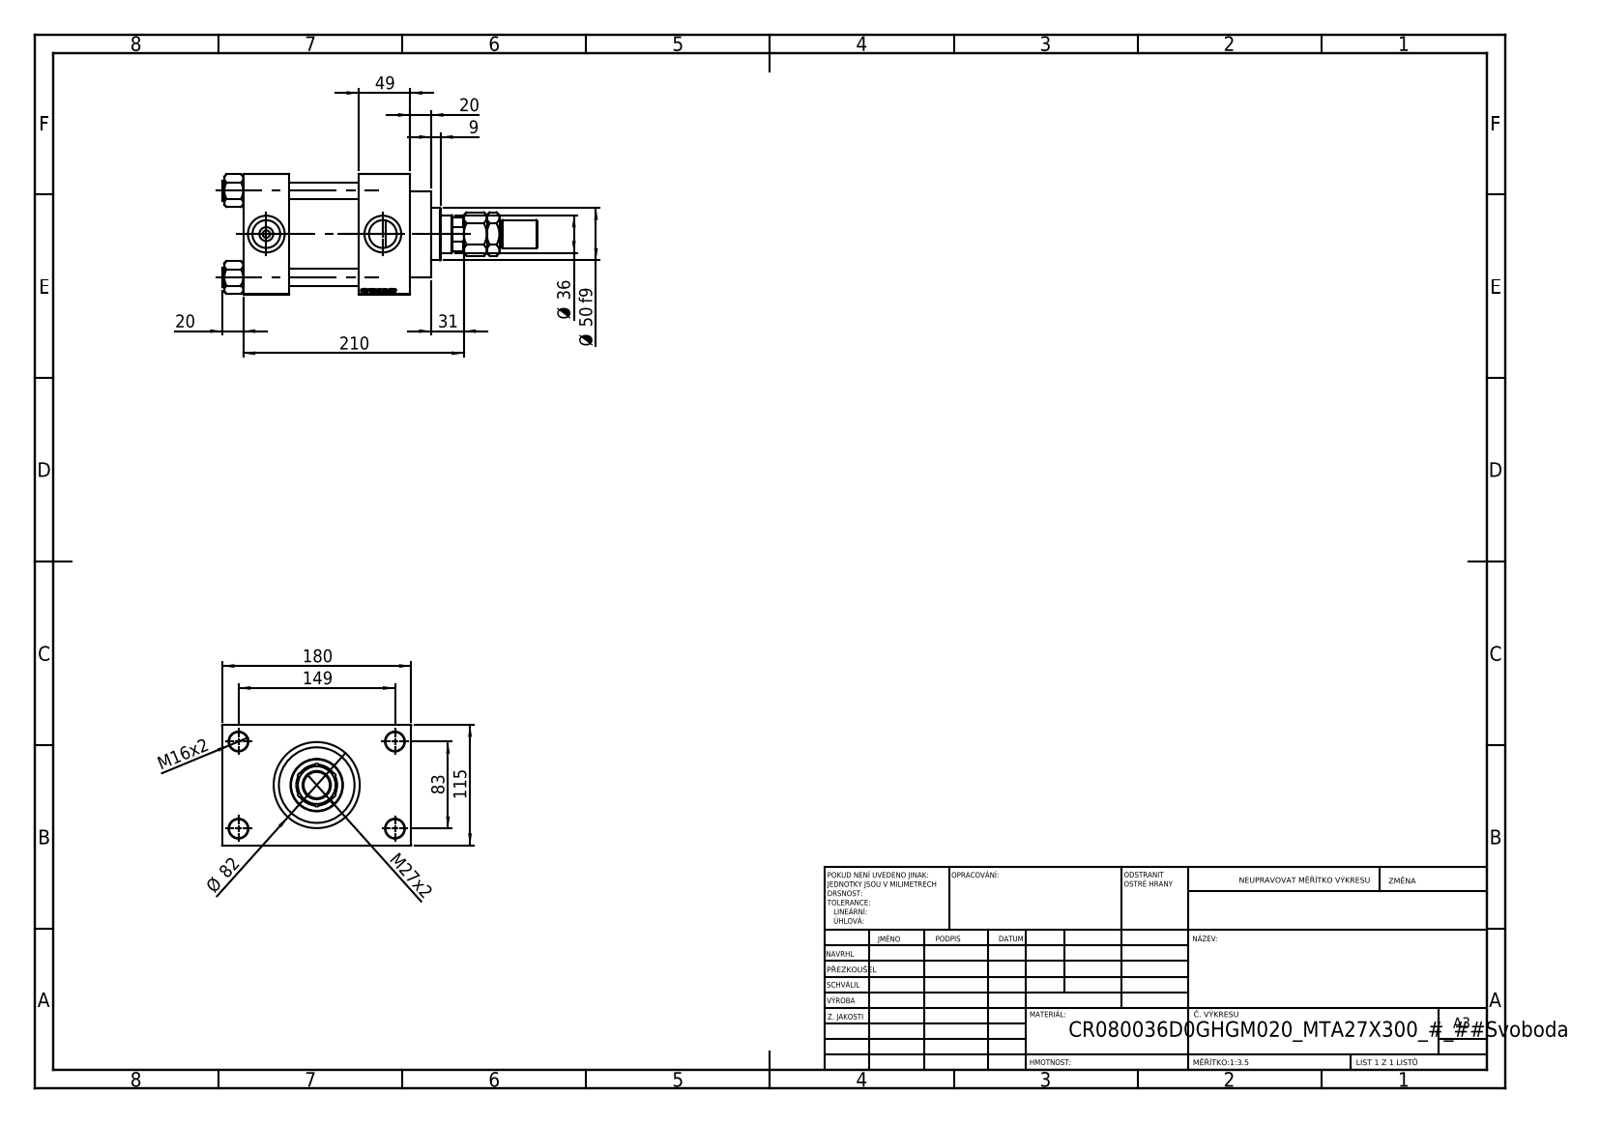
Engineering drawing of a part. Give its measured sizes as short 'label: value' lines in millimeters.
name: MTA; NUT_M5_D; V215_VC_A; V215CR_VCP_D (+2 more)
written by: SolidWorks 2019 (CONFIG_CONTROL_DESIGN)
unit: mm
bodies: 12 solids, 1200 faces (560 planar, 92 cylindrical, 548 other)
size: 300 × 180 × 115
volume: 2 038 000 mm³; area: 306 054 mm²
holes: 4× ⌀16, 4× ⌀18, 2× ⌀7, 2× ⌀26.44, 2× ⌀35, 1× ⌀25.5, 1× ⌀36, 1× ⌀39, 1× ⌀61, 1× ⌀72, 1× ⌀80
bosses: 4× ⌀19, 1× ⌀86, 1× ⌀82, 1× ⌀50, 1× ⌀27, 1× ⌀25
rounds: 1× R17.5
face distances: 115, 66, 110, 49, 44, 159, 32.5, 147.5, 20, 69
hole spacings: 33.15, 58.48, 82.7, 85.28, 89.24, 115.85, 142.43, 83
